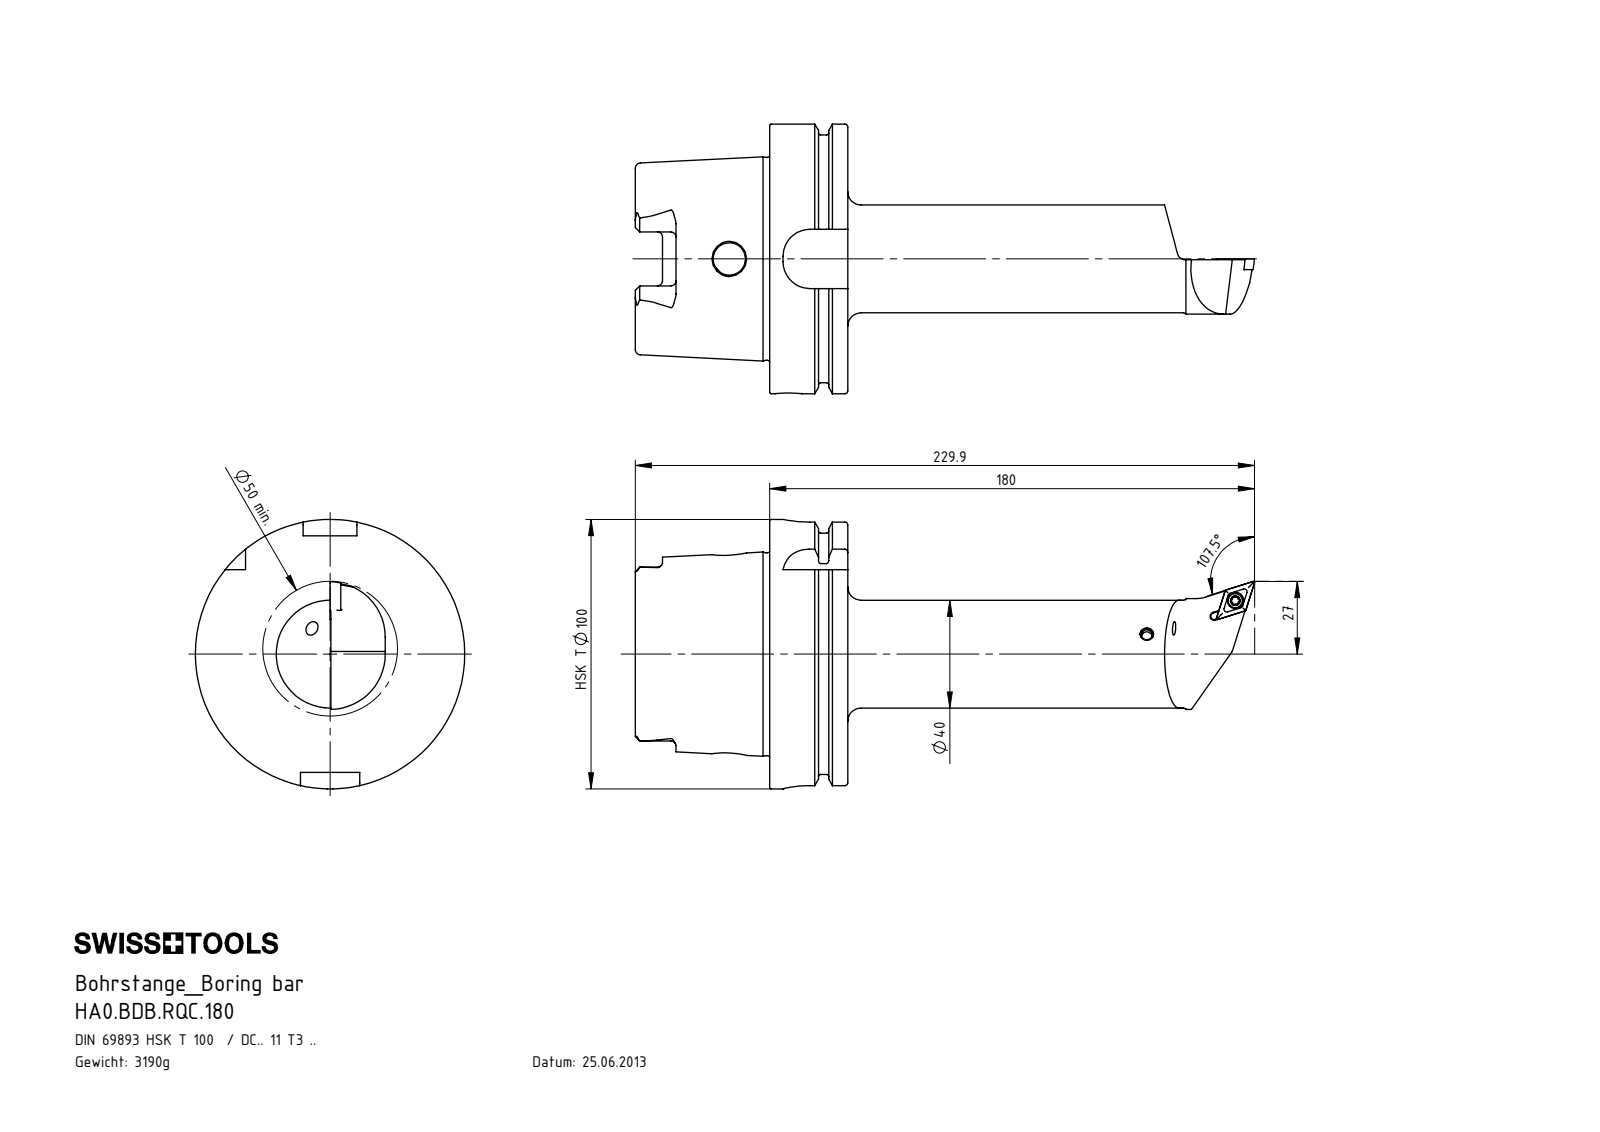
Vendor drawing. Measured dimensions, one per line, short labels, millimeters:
name: HA0-BDB.RQC.180_A_Fertigbearbeitung; WCB-ER2.001.009_A; DCMT11T304; HA0-BDB.RQC.180 (+1 more)
written by: SolidWorks 2017 (CONFIG_CONTROL_DESIGN)
unit: mm
bodies: 5 solids, 303 faces (74 planar, 88 cylindrical, 141 other)
size: 229.91 × 100 × 100
volume: 406 151 mm³; area: 72 263 mm²
holes: 2× ⌀4.2, 2× ⌀12, 1× ⌀3.3, 1× ⌀4, 1× ⌀4.4, 1× ⌀5, 1× ⌀6.1, 1× ⌀10, 1× ⌀22.5, 1× ⌀26, 1× ⌀53, 1× ⌀63
bosses: 1× ⌀100, 1× ⌀91.95, 1× ⌀75.26, 1× ⌀40, 1× ⌀5.25, 1× ⌀5, 1× ⌀4
rounds: 6× R0.34, 6× R0.59, 6× R1.9, 4× R10, 2× R4.83, 2× R4.88, 2× R20.5, 1× R1.25
face distances: 28.95, 12.45, 16.5, 49.9, 62.35, 78.85, 87.8, 78.2, 28.3, 15.85
hole spacings: 167.01, 167.11
